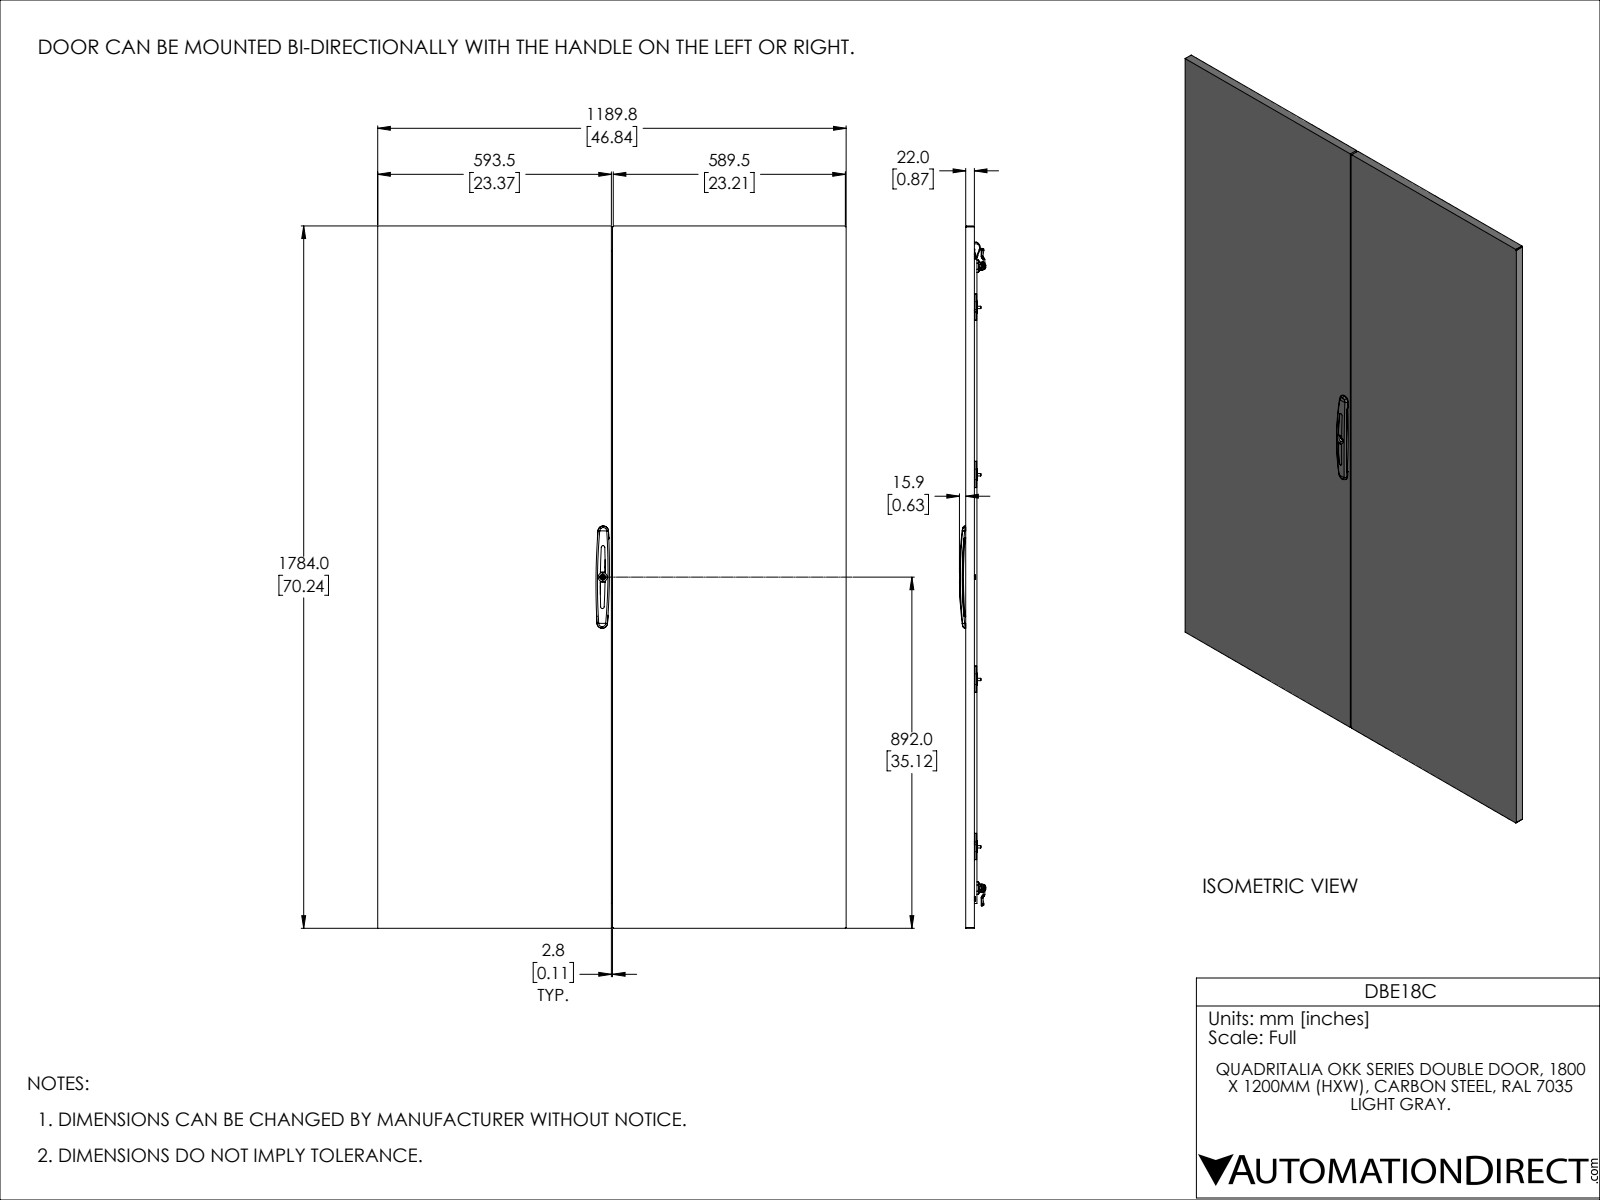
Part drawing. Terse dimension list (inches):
name: DBE18C
written by: SolidWorks 2021 (CONFIG_CONTROL_DESIGN)
unit: in
bodies: 175 solids, 5507 faces (2647 planar, 2005 cylindrical, 855 other)
size: 70.236 × 46.842 × 2.61
volume: 418.5 in³; area: 10 438 in²
holes: 272× ⌀0.167, 36× ⌀0.354, 24× ⌀0.01, 14× ⌀0.194, 12× ⌀0.276, 10× ⌀0.197, 8× ⌀0.244, 6× ⌀0.194, 4× ⌀0.156, 4× ⌀0.157, 3× ⌀0.205, 3× ⌀0.402
bosses: 40× ⌀0.276, 36× ⌀0.236, 20× ⌀0.283, 8× ⌀0.472, 8× ⌀0.193, 4× ⌀0.138, 3× ⌀0.598, 3× ⌀0.504
rounds: 116× R0.059, 93× R0.02, 84× R0.039, 74× R0.012, 44× R0.177, 35× R0.079, 28× R0.098, 20× R0.008
face distances: 0.079, 0.059, 0.728, 0.787, 23.476, 0.669, 0.866, 1.043, 23.287, 0.138
hole spacings: 0.984, 1.969, 2.953, 8.858, 3.937, 4.921, 5.906, 6.89
